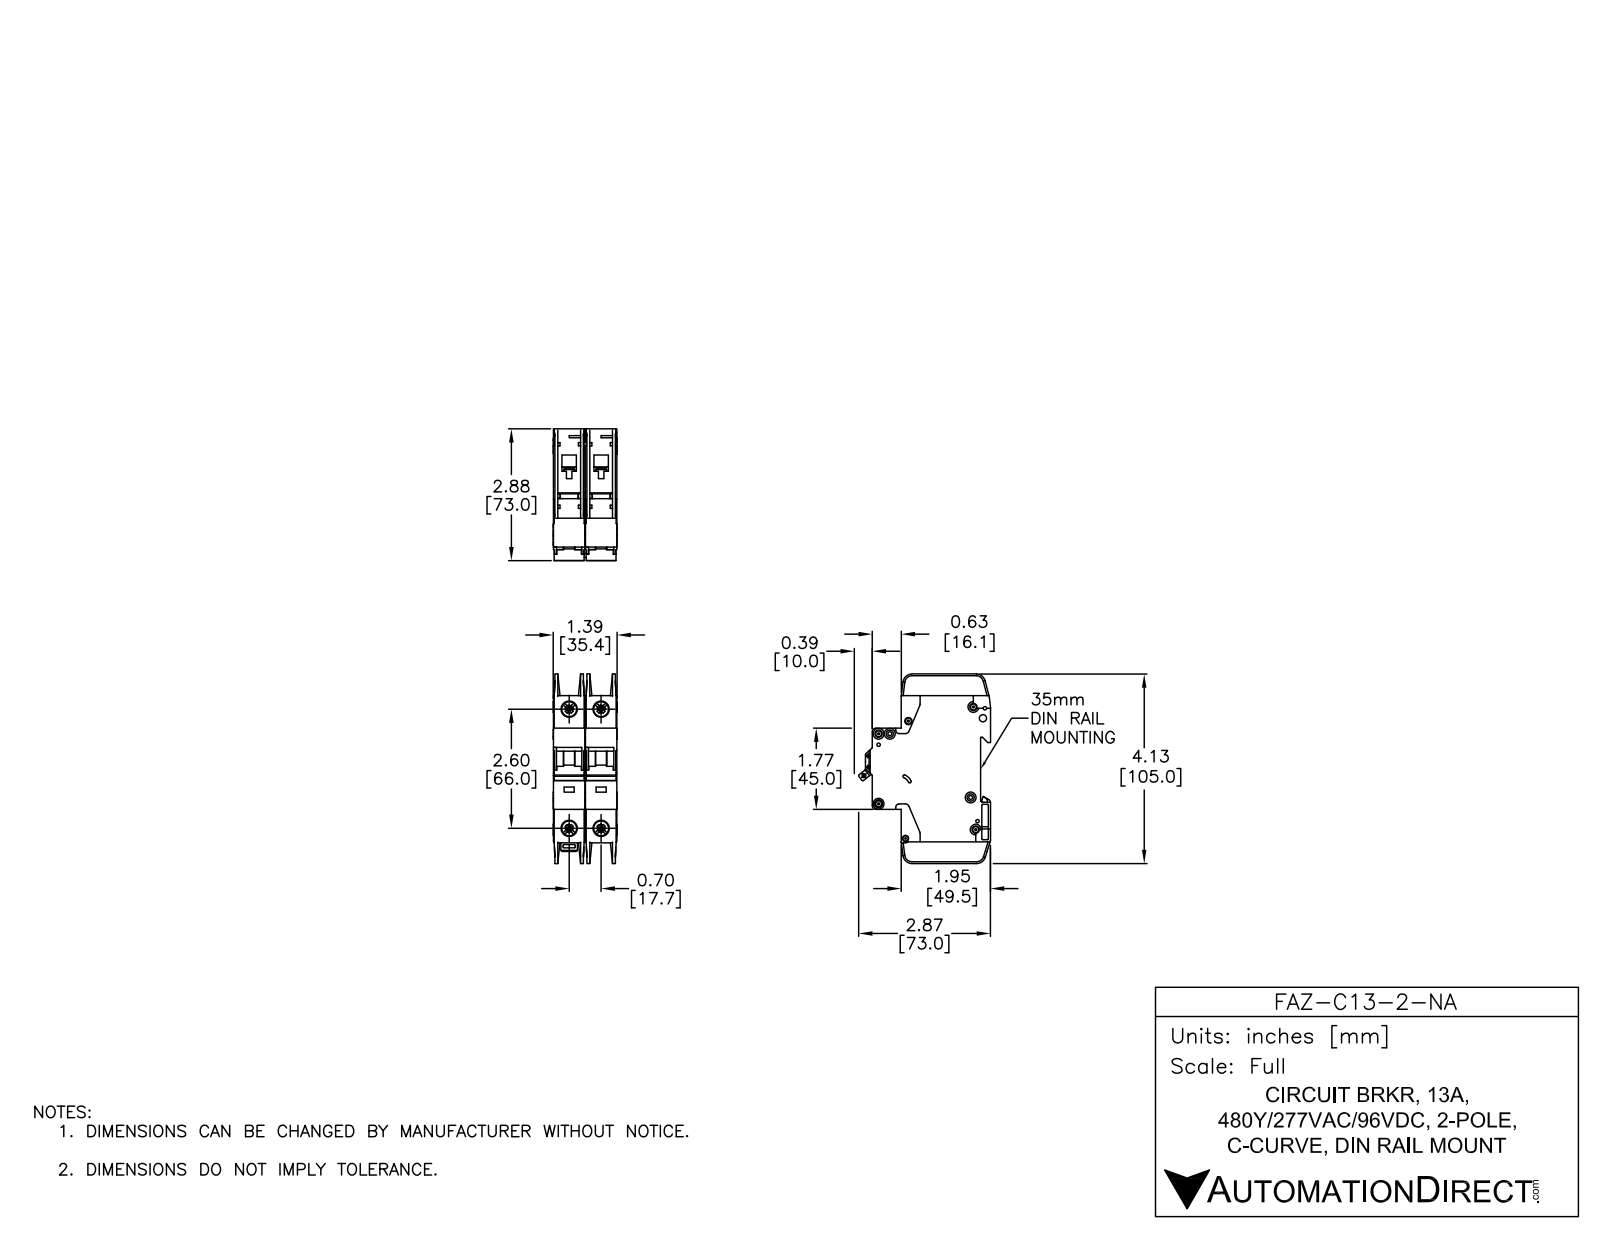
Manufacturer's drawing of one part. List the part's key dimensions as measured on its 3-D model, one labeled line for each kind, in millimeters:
Part name (STEP PRODUCT): FAZ-C13-2-NA
STEP written by: SolidWorks 2014 (AUTOMOTIVE_DESIGN)
Units: millimetres
Bodies: 6 solids, 1568 faces (818 planar, 526 cylindrical, 224 other)
Overall size (bounding box): 105 × 73.04 × 35.4
Volume: 155 390 mm³ · Surface area: 49 479 mm²
Round holes (diameter × count): ⌀3.6 ×7, ⌀7.15 ×4, ⌀8.2 ×4, ⌀1.09 ×2, ⌀1.5 ×2, ⌀4 ×2, ⌀1.9 ×1, ⌀2.15 ×1, ⌀2.2 ×1, ⌀2.55 ×1, ⌀3.3 ×1, ⌀3.4 ×1
Round bosses / shafts (diameter × count): ⌀6 ×7, ⌀2.5 ×2
Partial cylindrical surfaces — rounded edges, fillets, slot ends (radius × count): R0.25 ×47, R0.5 ×24, R1 ×18, R2 ×12, R5 ×5, R1.8 ×4, R4 ×4, R0.2 ×2
Main face-to-face distances: 17.7, 17.5, 0.7, 15.05, 2.45, 1.75, 15.75, 13.3, 35.2, 17
Hole centre spacings: 6.2, 17.7, 66, 68.33, 5.19, 6.1, 8.19, 8.56
